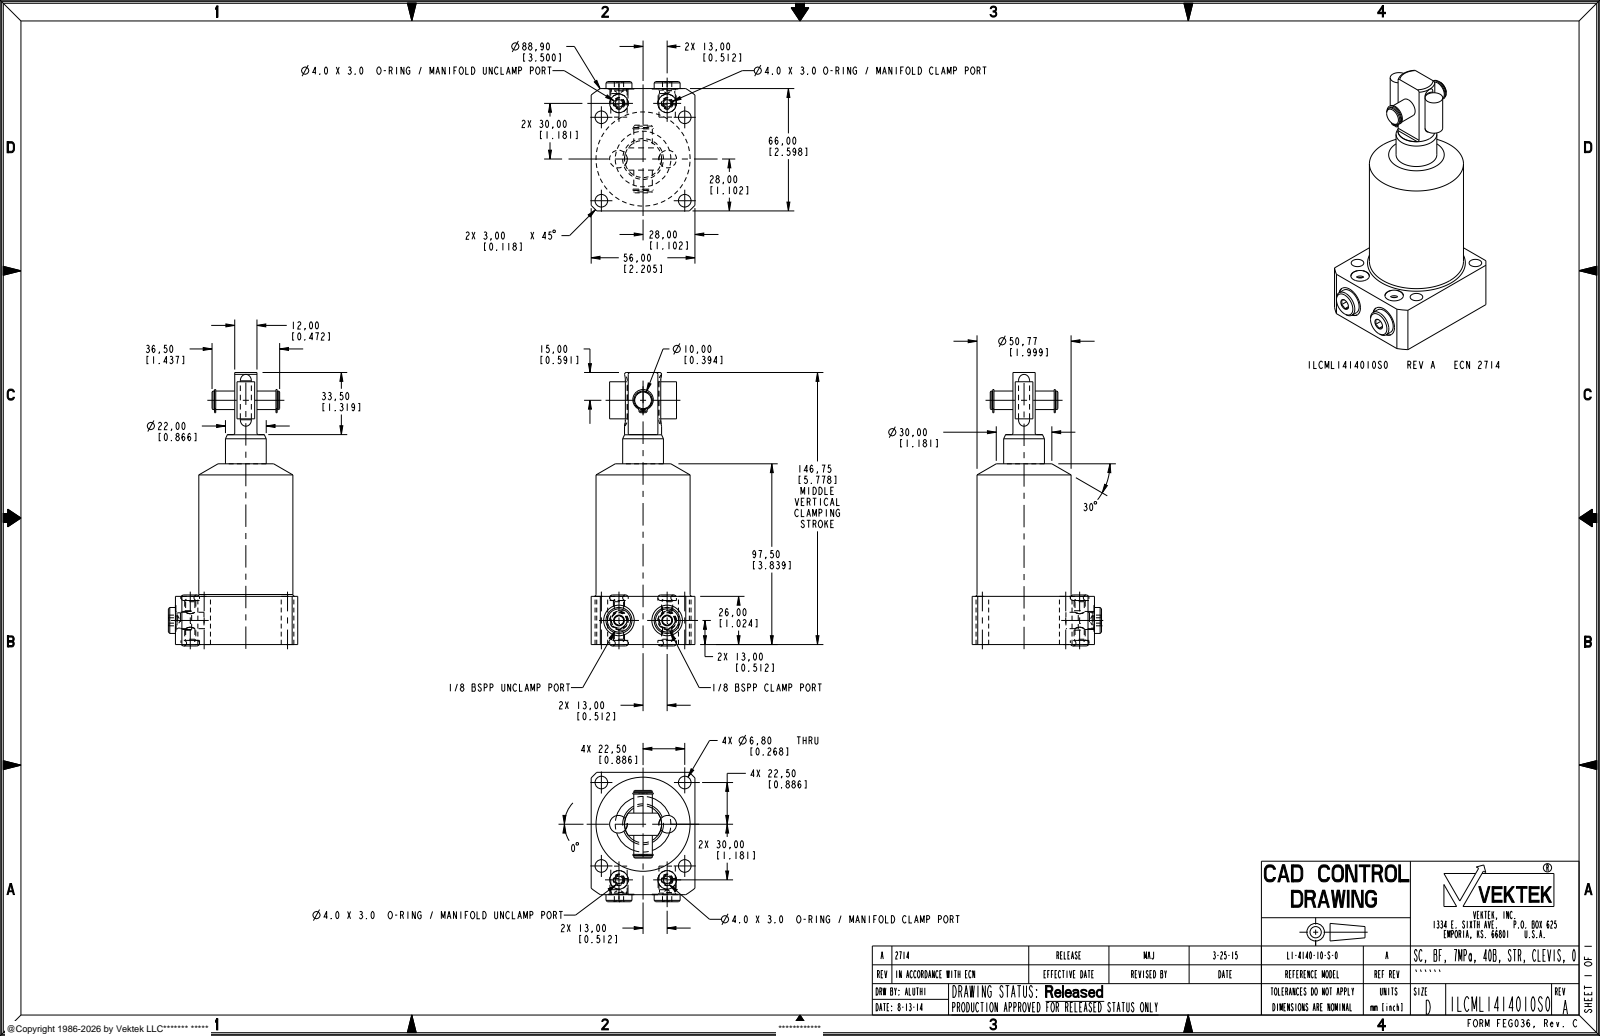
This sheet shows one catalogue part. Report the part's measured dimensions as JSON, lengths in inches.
{"part_name": "ILCML1414010S0", "step_written_by": "PRO/ENGINEER BY PARAMETRIC TECHNOLOGY CORPORATION, 2013320 (AUTOMOTIVE_DESIGN)", "units": "inches", "bodies": {"solids": 7, "faces": 234, "planar": 80, "cylindrical": 98, "other": 56}, "overall_size": [5.807, 2.748, 2.205], "volume_in3": 15.18, "surface_area_in2": 54.96, "round_holes": [[0.268, 4], [0.041, 2], [0.197, 2], [0.348, 2], [0.394, 2], [0.65, 2]], "round_bosses_or_shafts": [[0.551, 2], [0.383, 2], [0.375, 2], [0.325, 2], [0.236, 2], [1.999, 1], [0.866, 1], [0.787, 1]], "partial_cylinders_radius": [[0.031, 2], [0.041, 2], [0.058, 2], [0.187, 2], [1.75, 1]], "face_to_face_distances": [2.205, 1.024, 2.598, 0.866, 1.732, 1.339, 0.472, 1.26, 3.839, 2.815], "hole_center_spacings": [1.772, 0.476, 1.024, 1.428, 2.1, 2.495, 2.506, 4.477]}
